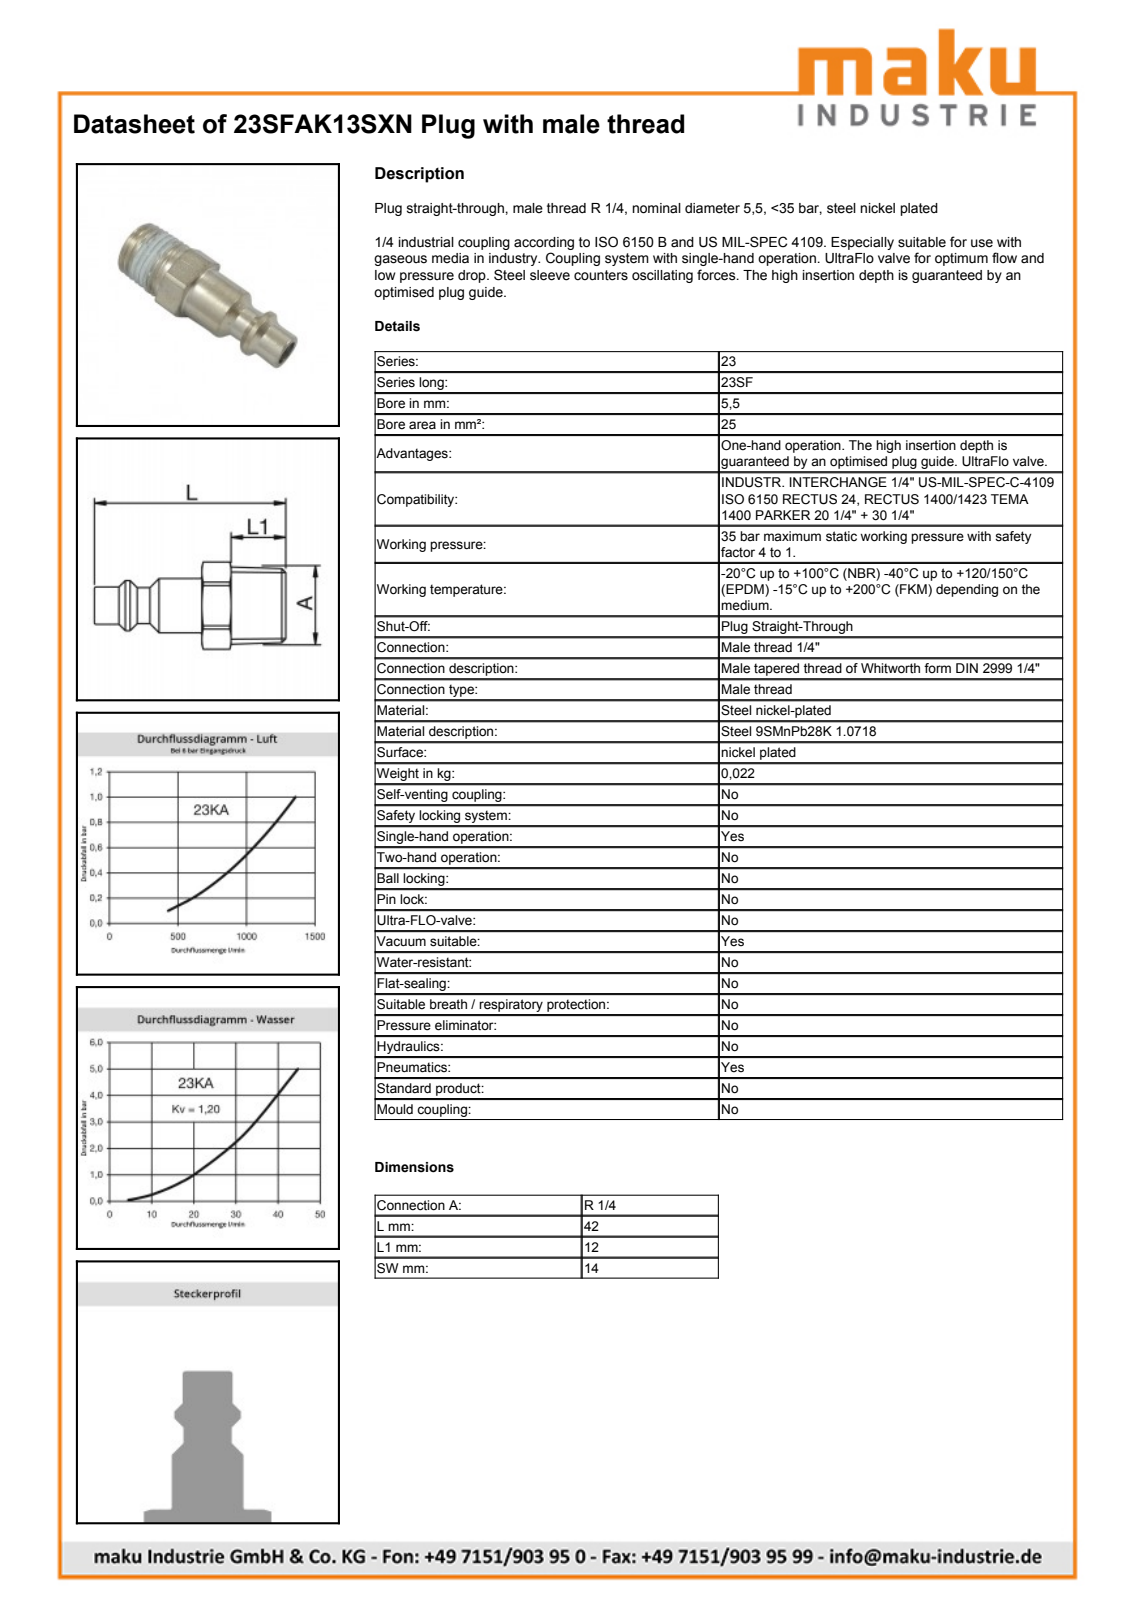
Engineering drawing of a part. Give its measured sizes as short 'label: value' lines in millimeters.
name: D108572
written by: Autodesk Inventor 2013 (AUTOMOTIVE_DESIGN)
unit: mm
bodies: 1 solid, 43 faces (10 planar, 12 cylindrical, 21 other)
size: 42 × 15.8 × 14
volume: 2 724 mm³; area: 2 578 mm²
holes: 1× ⌀5.5, 1× ⌀7.5
bosses: 1× ⌀11.8, 1× ⌀10.9, 1× ⌀8.1, 1× ⌀7.8
rounds: 1× R7.9
face distances: 14, 6.4, 23.6, 30, 42, 18.4, 12
